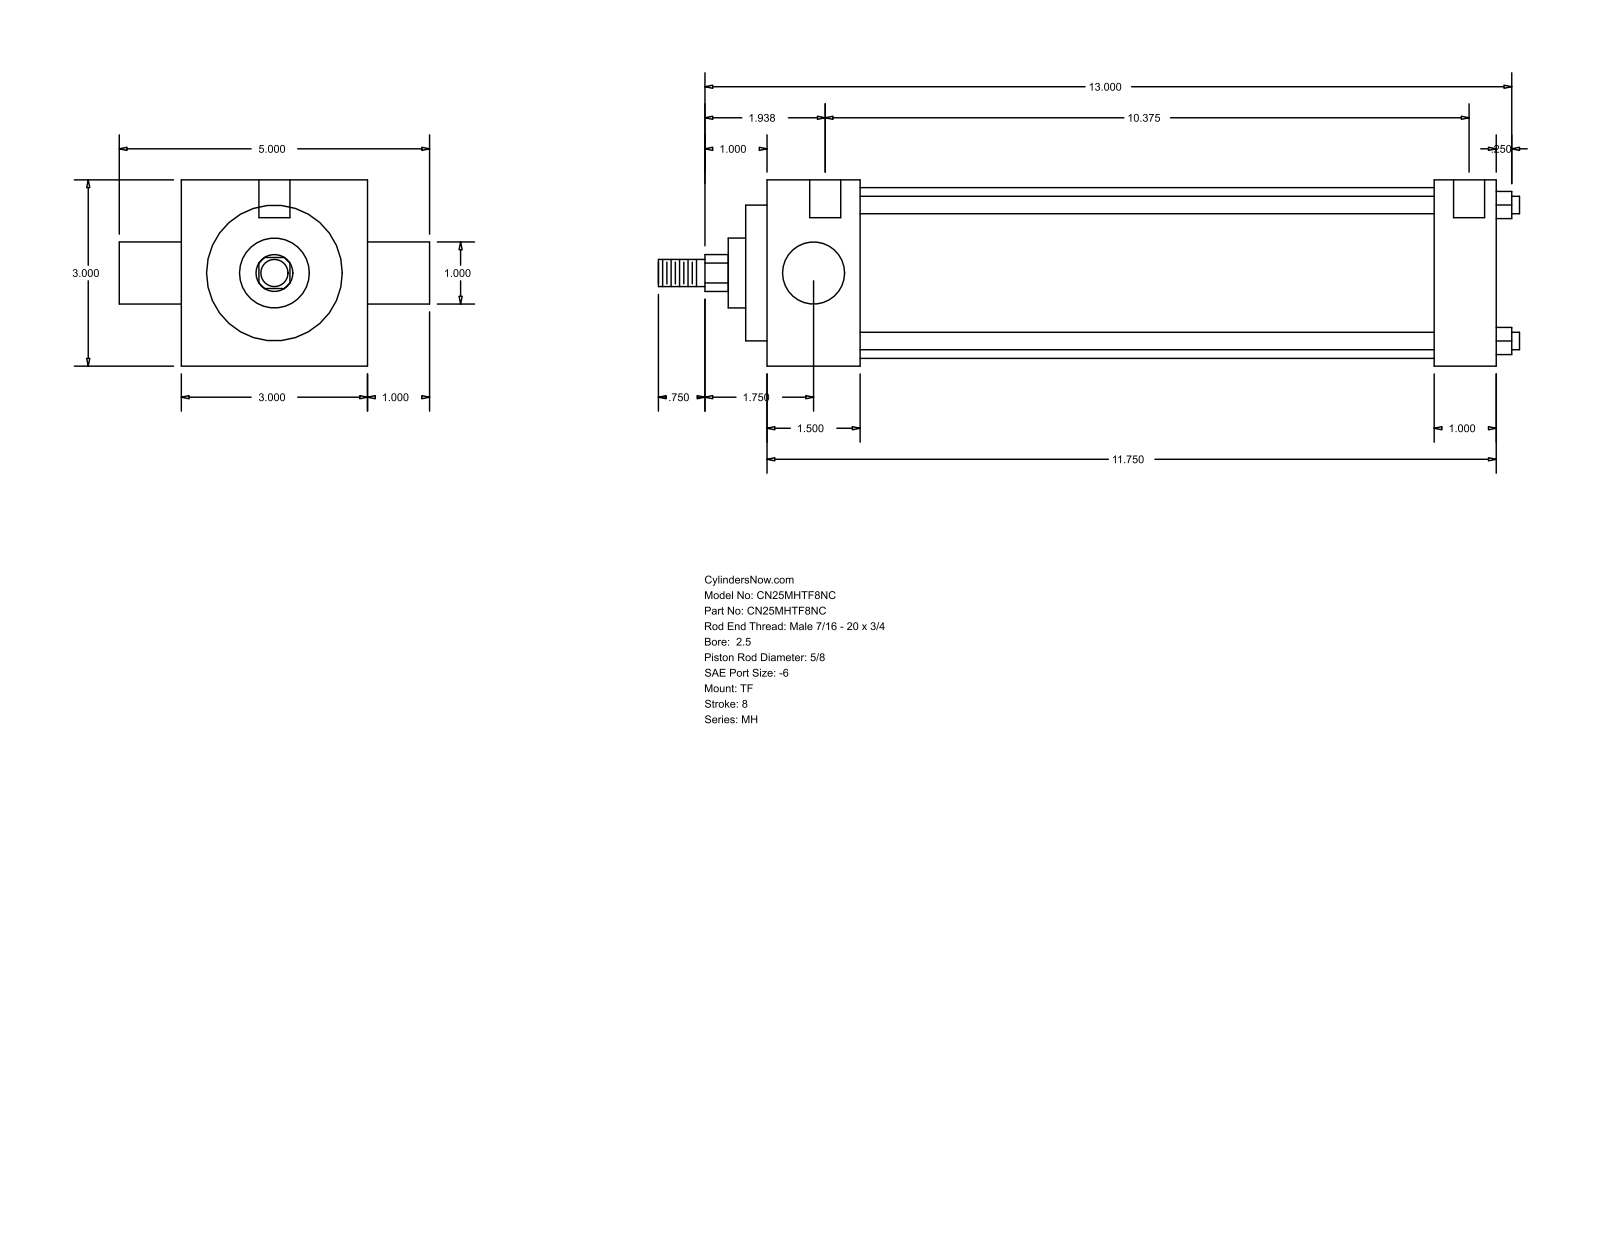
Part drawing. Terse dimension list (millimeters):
name: MH_TF__0250_0.625
written by: GSSL Pune (CONFIG_CONTROL_DESIGN)
unit: mm
bodies: 0 solids, 86 faces (61 planar, 25 cylindrical, 0 other)
size: 352.43 × 127 × 76.2
holes: 3× ⌀5.56, 2× ⌀12.7
bosses: 4× ⌀7.14, 1× ⌀69.85, 1× ⌀55.55, 1× ⌀28.57, 1× ⌀25.4, 1× ⌀15.88, 1× ⌀11.11
rounds: 1× R7.54
face distances: 76.2, 298.45, 25.4, 38.1, 260.35, 273.05, 234.95, 8.73, 46.83, 281.78
hole spacings: 3.17, 4.76, 263.53, 266.7, 268.29, 271.46
